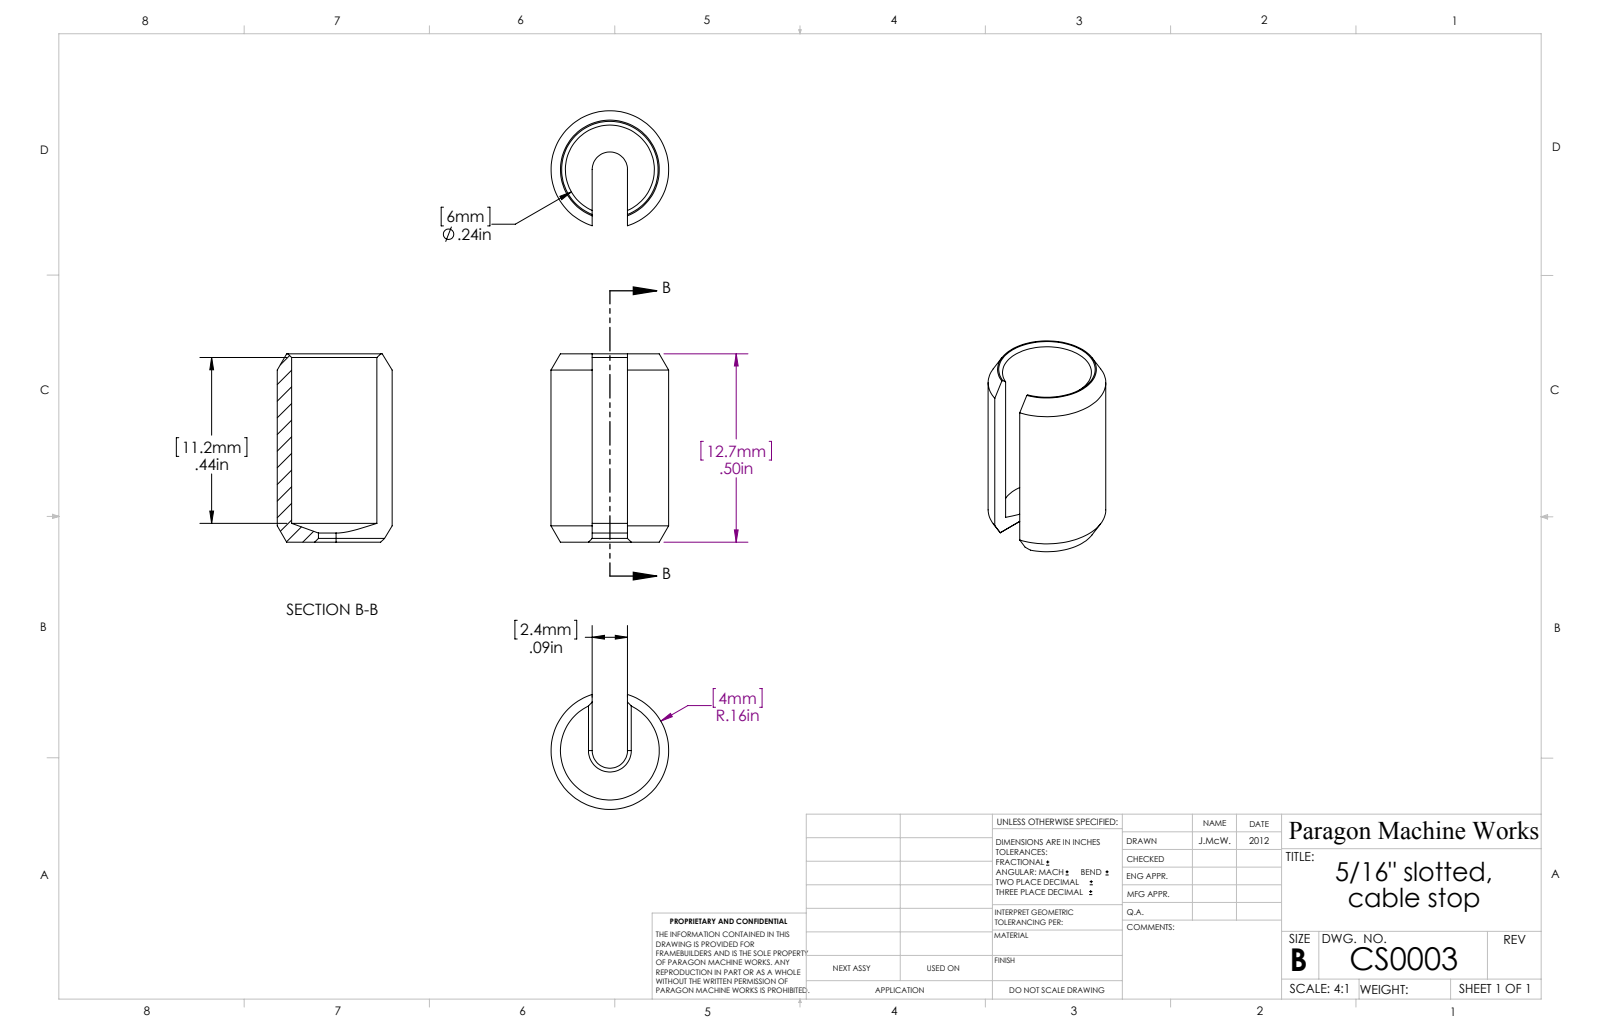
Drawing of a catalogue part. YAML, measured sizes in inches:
part_name: "CS0003"
step_written_by: "SolidWorks 2023 (AUTOMOTIVE_DESIGN)"
units: inches
bodies: {solids: 1, faces: 13, planar: 4, cylindrical: 5, other: 4}
overall_size: [0.5, 0.313, 0.305]
volume: 0.015
surface_area: 0.866
round_holes:
  - {diameter: 0.236, count: 1}
round_bosses_or_shafts:
  - {diameter: 0.313, count: 1}
partial_cylinders:
  - {radius: 0.047, count: 1}
face_to_face_distances: [0.094, 0.5]
